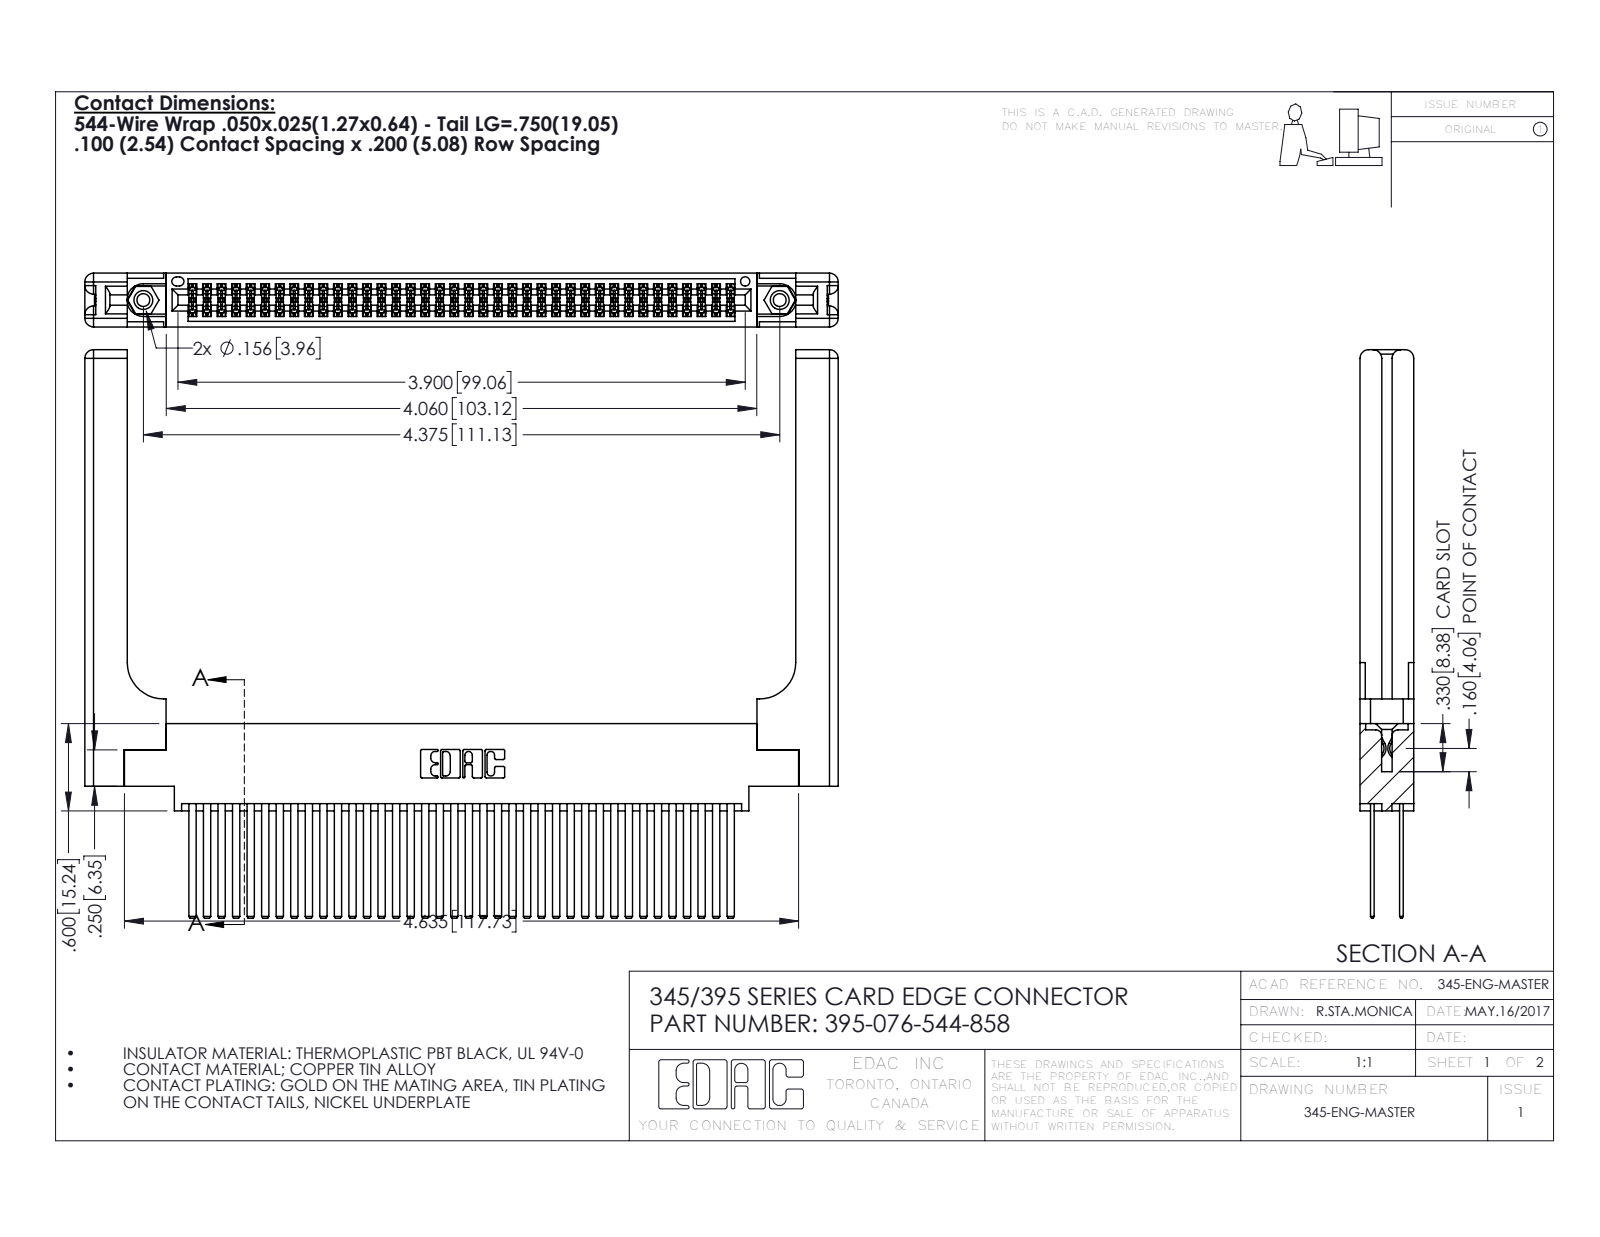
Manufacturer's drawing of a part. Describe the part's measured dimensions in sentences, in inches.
The part is named "345-292-001_345-293-144; 345 Part_0.170 Offset - 0.156 Dia-TH; 345-220-058_345-220-058; 345-250-001_345-250-001-102 (+1 more)". Its 3-D file was written by "SolidWorks 2016 (CONFIG_CONTROL_DESIGN)". It is 81 solids with 3730 faces: 2436 planar, 1234 cylindrical and 60 other. Overall it measures 5.179 by 3.907 by 0.37 inches. Its volume is 1.353 cubic inches and its surface area 44.16 square inches. Round holes: 2 of diameter 0.089, 2 of diameter 0.125, 2 of diameter 0.156, 1 of diameter 0.064. Round bosses or shafts: 2 of diameter 0.155. Partial cylindrical surfaces (rounded edges, fillets, slot ends): 114 of radius 0.006, 22 of radius 0.01, 16 of radius 0.06, 6 of radius 0.007, 6 of radius 0.031, 3 of radius 0.026, 2 of radius 0.014, 2 of radius 0.019. The main face-to-face distances are 0.072, 0.298, 0.098, 0.272, 0.025, 0.2, 0.37, 0.225, 0.175, 0.148. The hole center spacings are 0.27, 4.139, 4.375.
